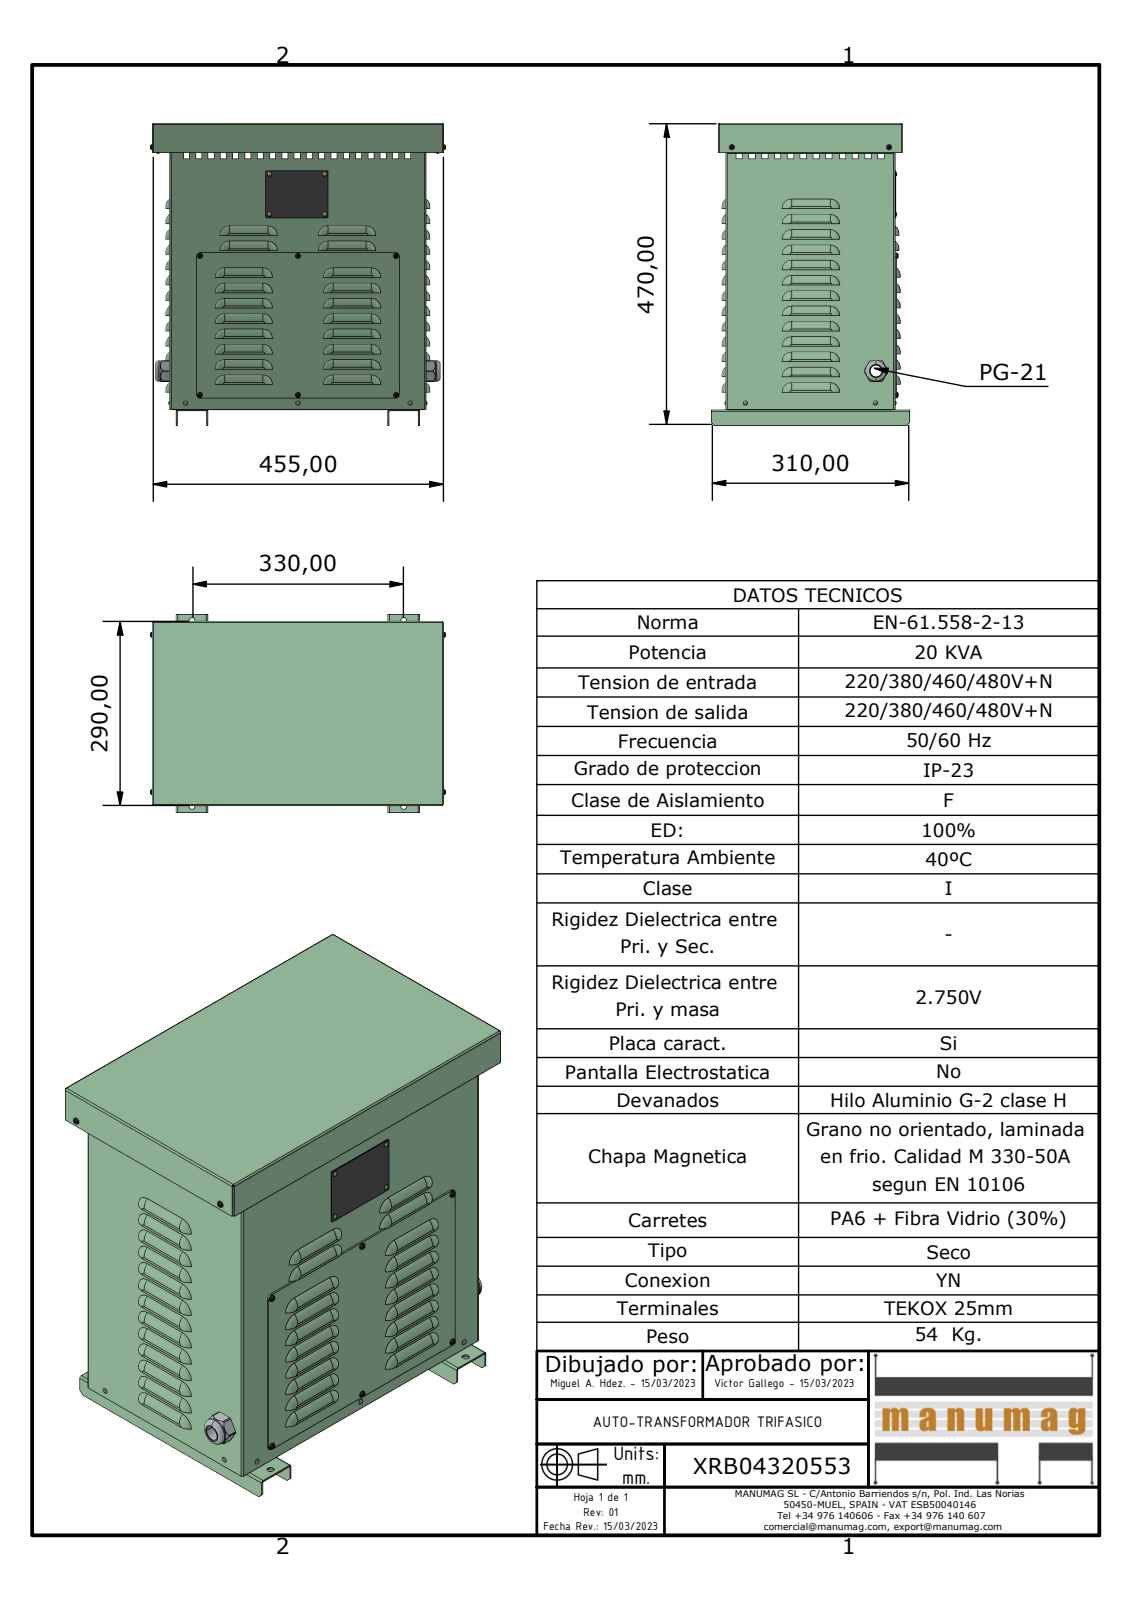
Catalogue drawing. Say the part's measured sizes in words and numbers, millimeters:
The part is named "XRB04320553; JE015 - JE020 - JE025 EXPORT CUERPO; JE015 - JE020 - JE025 EXPORT BASE; JE015 - JE020 - JE025 EXPORT PATA (+6 more)". Its 3-D file was written by "Autodesk Inventor 2023 (AUTOMOTIVE_DESIGN)". It is 33 solids with 2242 faces: 1225 planar, 489 cylindrical and 528 other. Overall it measures 474.44 by 463.69 by 310 millimeters. Its volume is 2 342 000 cubic millimeters and its surface area 2 098 000 square millimeters. Round holes: 17 of diameter 3.4, 9 of diameter 4, 8 of diameter 2.3, 6 of diameter 9, 3 of diameter 5.1, 2 of diameter 8.92, 1 of diameter 18, 1 of diameter 29.9. Round bosses or shafts: 9 of diameter 3.2, 8 of diameter 4, 8 of diameter 3.62, 1 of diameter 32.4, 1 of diameter 28.5, 1 of diameter 28.3. Partial cylindrical surfaces (rounded edges, fillets, slot ends): 118 of radius 14, 63 of radius 4, 49 of radius 15, 10 of radius 2, 9 of radius 2, 8 of radius 3.47, 6 of radius 0.5, 6 of radius 2.5. The main face-to-face distances are 2, 262.92, 264.92, 400.8, 447.27, 449.27, 260.92, 398.8, 402.8, 4. The hole center spacings are 218.1, 153.8, 154.1, 266.87, 267.05, 307.9, 332.28, 377.32.
